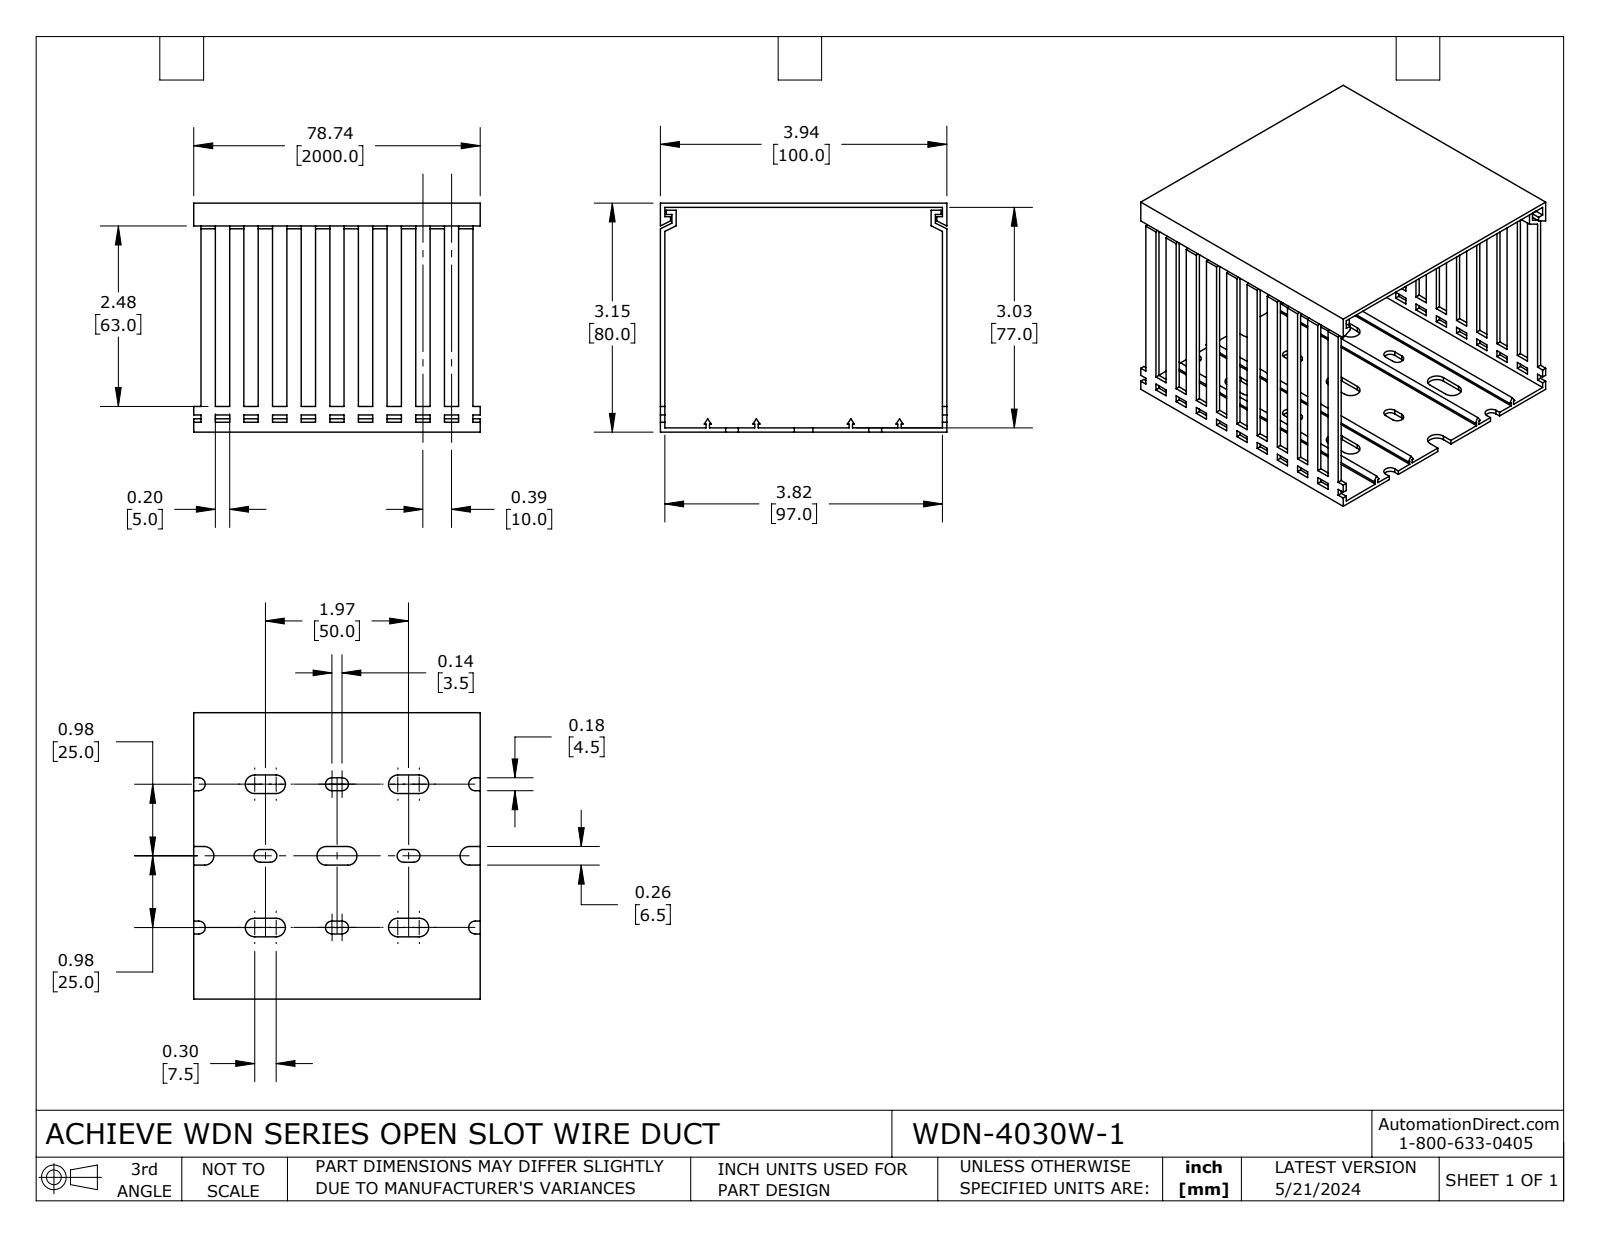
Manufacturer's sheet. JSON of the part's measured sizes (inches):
{"part_name": "WDN-4030W-1", "step_written_by": "SolidWorks 2023 (CONFIG_CONTROL_DESIGN)", "units": "inches", "bodies": {"solids": 2, "faces": 412, "planar": 376, "cylindrical": 36, "other": 0}, "overall_size": [3.937, 3.937, 3.15], "volume_in3": 2.806, "surface_area_in2": 105.9, "partial_cylinders_radius": [[0.089, 12], [0.128, 12]], "face_to_face_distances": [0.059, 3.091, 3.15, 3.031, 3.878, 3.937, 3.819, 0.394, 0.197, 0.591]}
